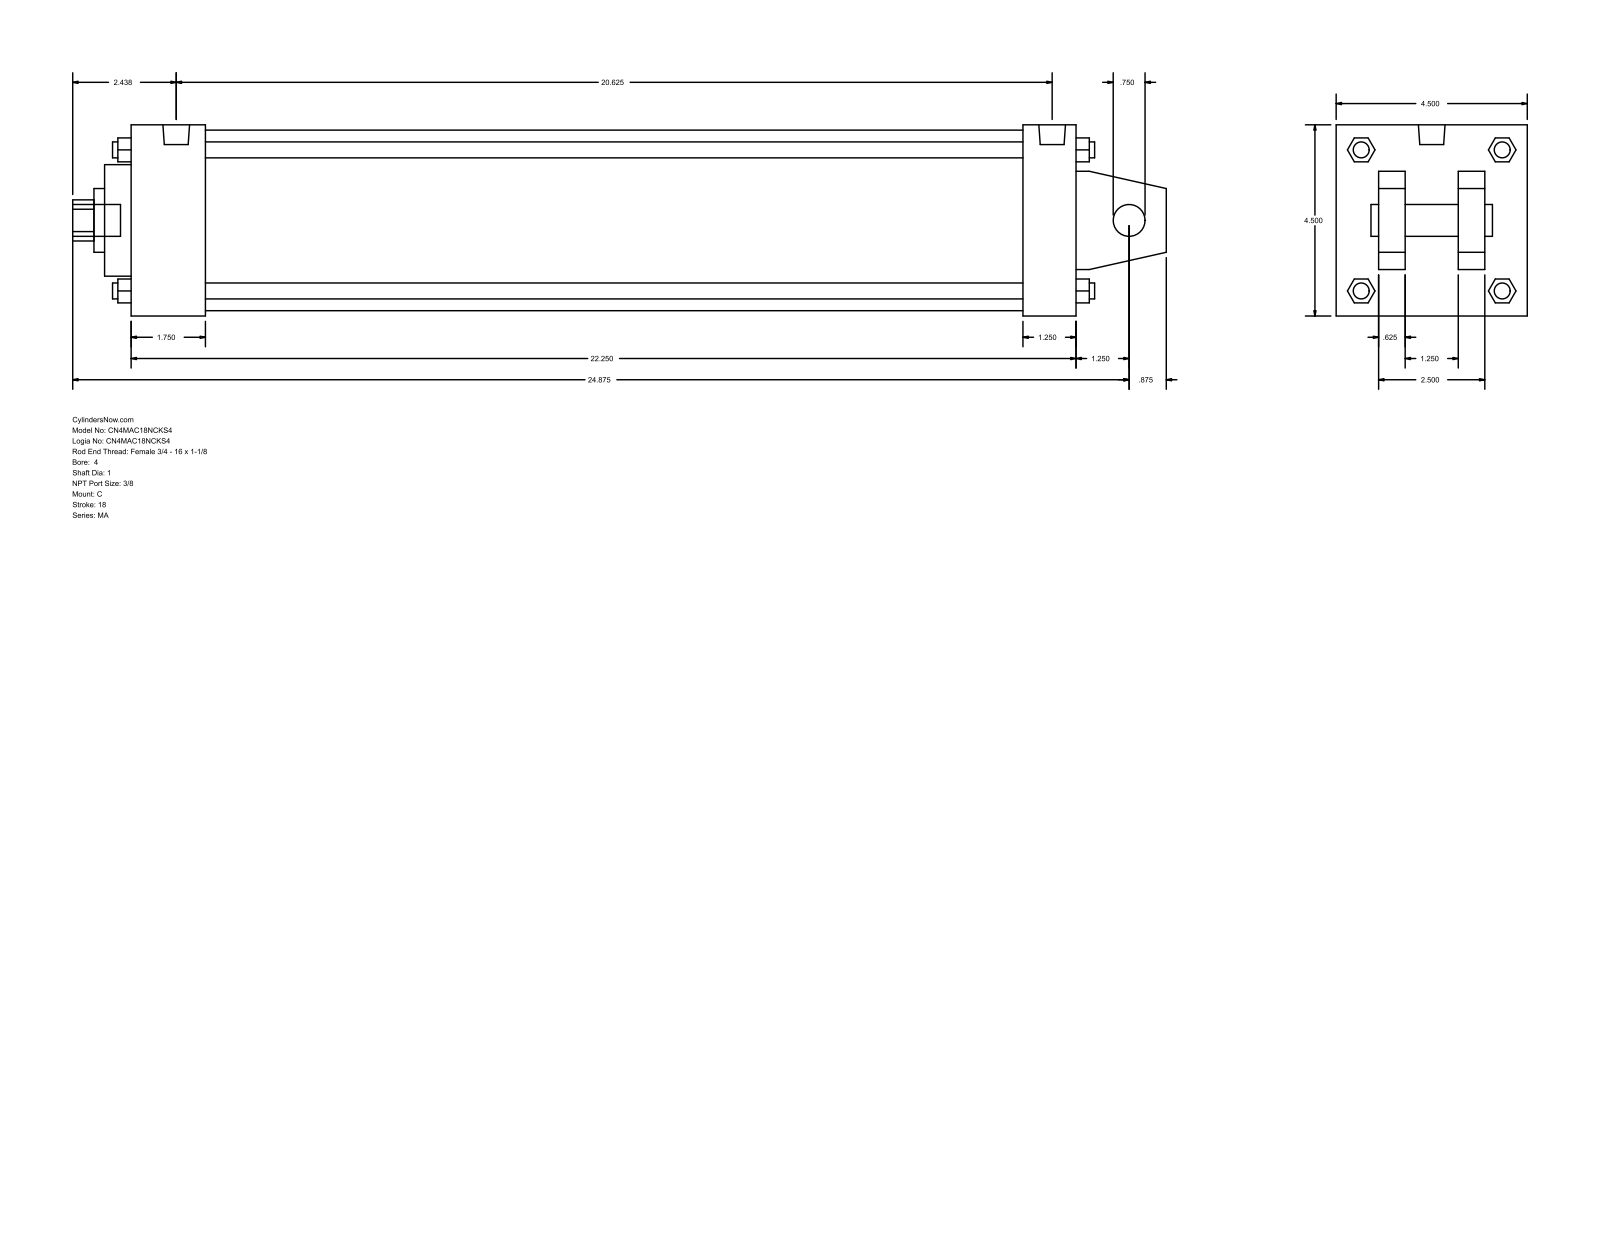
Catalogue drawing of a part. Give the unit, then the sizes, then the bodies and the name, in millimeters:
Units: millimetres
Overall size (bounding box): 654.05 × 114.3 × 114.3
Round holes (diameter × count): ⌀19.05 ×1, ⌀25.4 ×1, ⌀38.1 ×1, ⌀66.67 ×1, ⌀107.95 ×1
Round bosses / shafts (diameter × count): ⌀11.11 ×4, ⌀9.53 ×4, ⌀15.93 ×2, ⌀19.05 ×1
Partial cylindrical surfaces — rounded edges, fillets, slot ends (radius × count): R12.29 ×1
Main face-to-face distances: 114.3, 565.16, 15.87, 73.03, 41.27, 25.4, 88.9, 47.63, 533.41, 31.75
Bodies: 0 solids, 141 faces (109 planar, 32 cylindrical, 0 other)
Part name (STEP PRODUCT): MA_C__0400_1
STEP written by: GSSL Pune (CONFIG_CONTROL_DESIGN)
